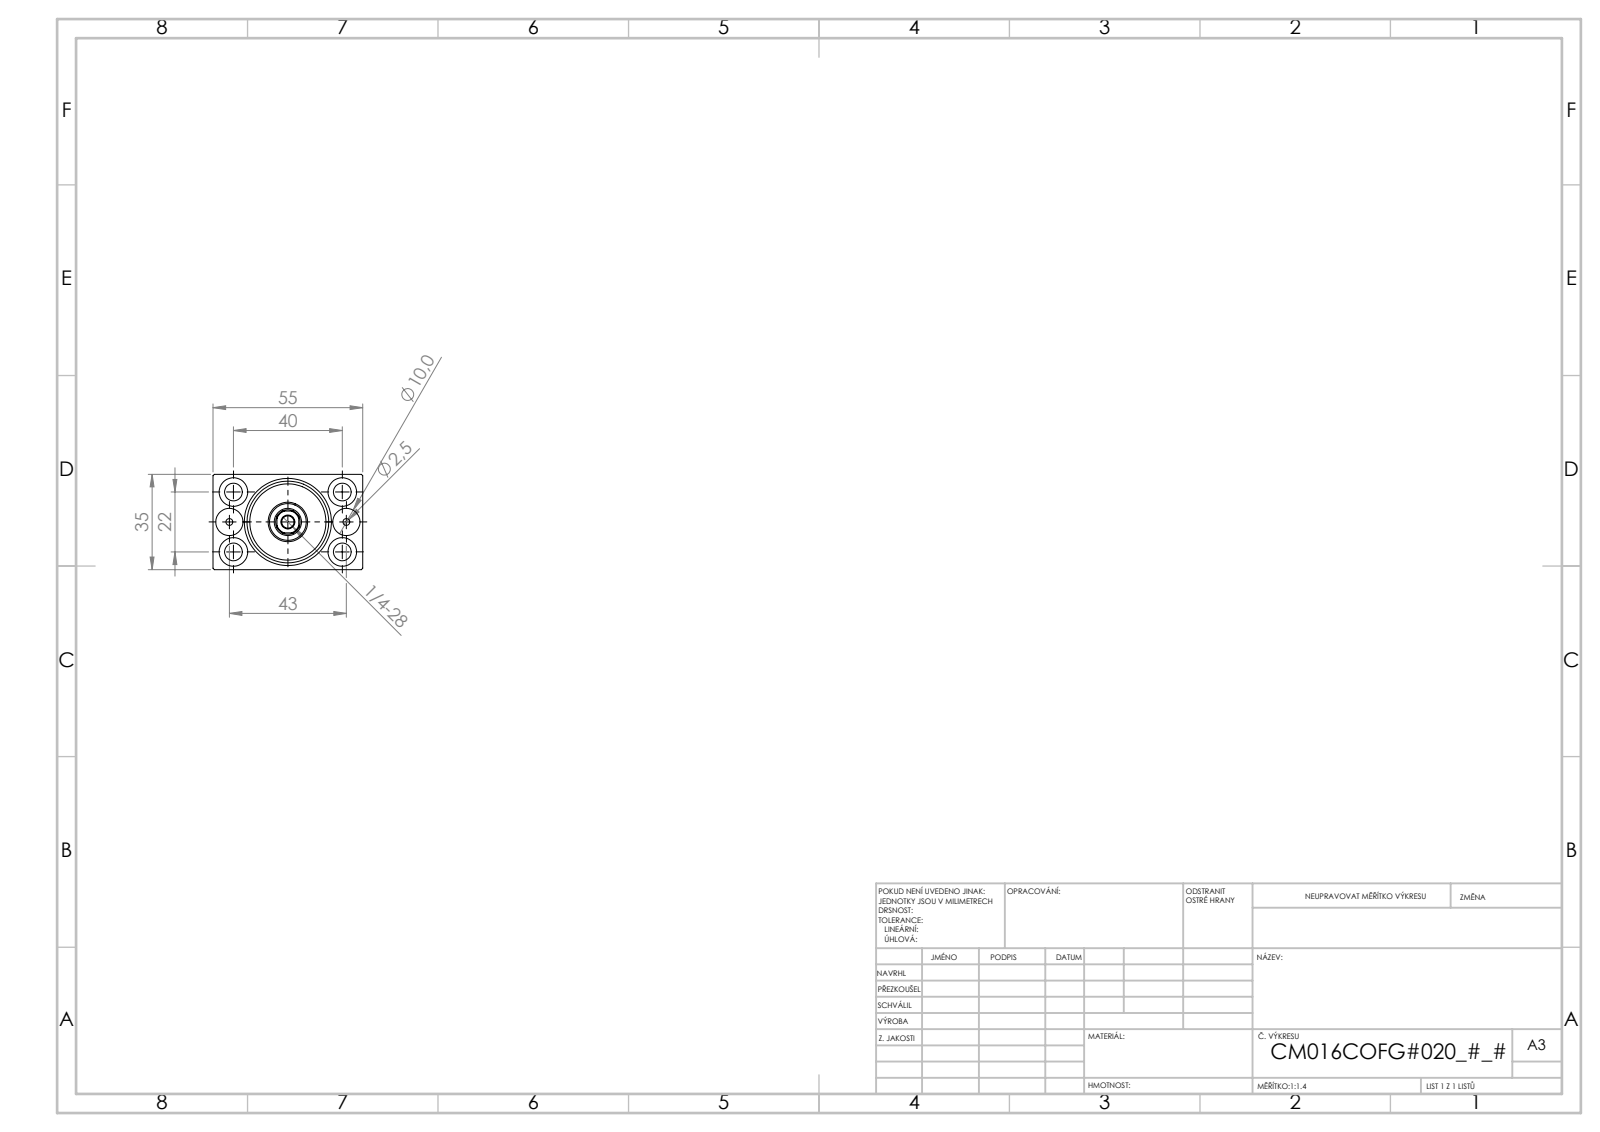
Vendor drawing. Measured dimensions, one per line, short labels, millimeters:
name: V450CM_C_Body; V450CM_C_VCP; V450CM_VC_B
written by: SolidWorks 2019 (CONFIG_CONTROL_DESIGN)
unit: mm
bodies: 3 solids, 861 faces (409 planar, 58 cylindrical, 394 other)
size: 75 × 55 × 35
volume: 113 034 mm³; area: 30 036 mm²
holes: 4× ⌀6.5, 4× ⌀10.5, 3× ⌀10, 2× ⌀2.5, 1× ⌀4.5, 1× ⌀13.5, 1× ⌀14.5, 1× ⌀16, 1× ⌀18, 1× ⌀30
rounds: 1× R4.5
face distances: 35, 55, 5, 61, 3, 66, 10, 8, 31.5, 69
hole spacings: 11.1, 22.83, 42.93, 21.5, 22, 40, 45.65, 43
